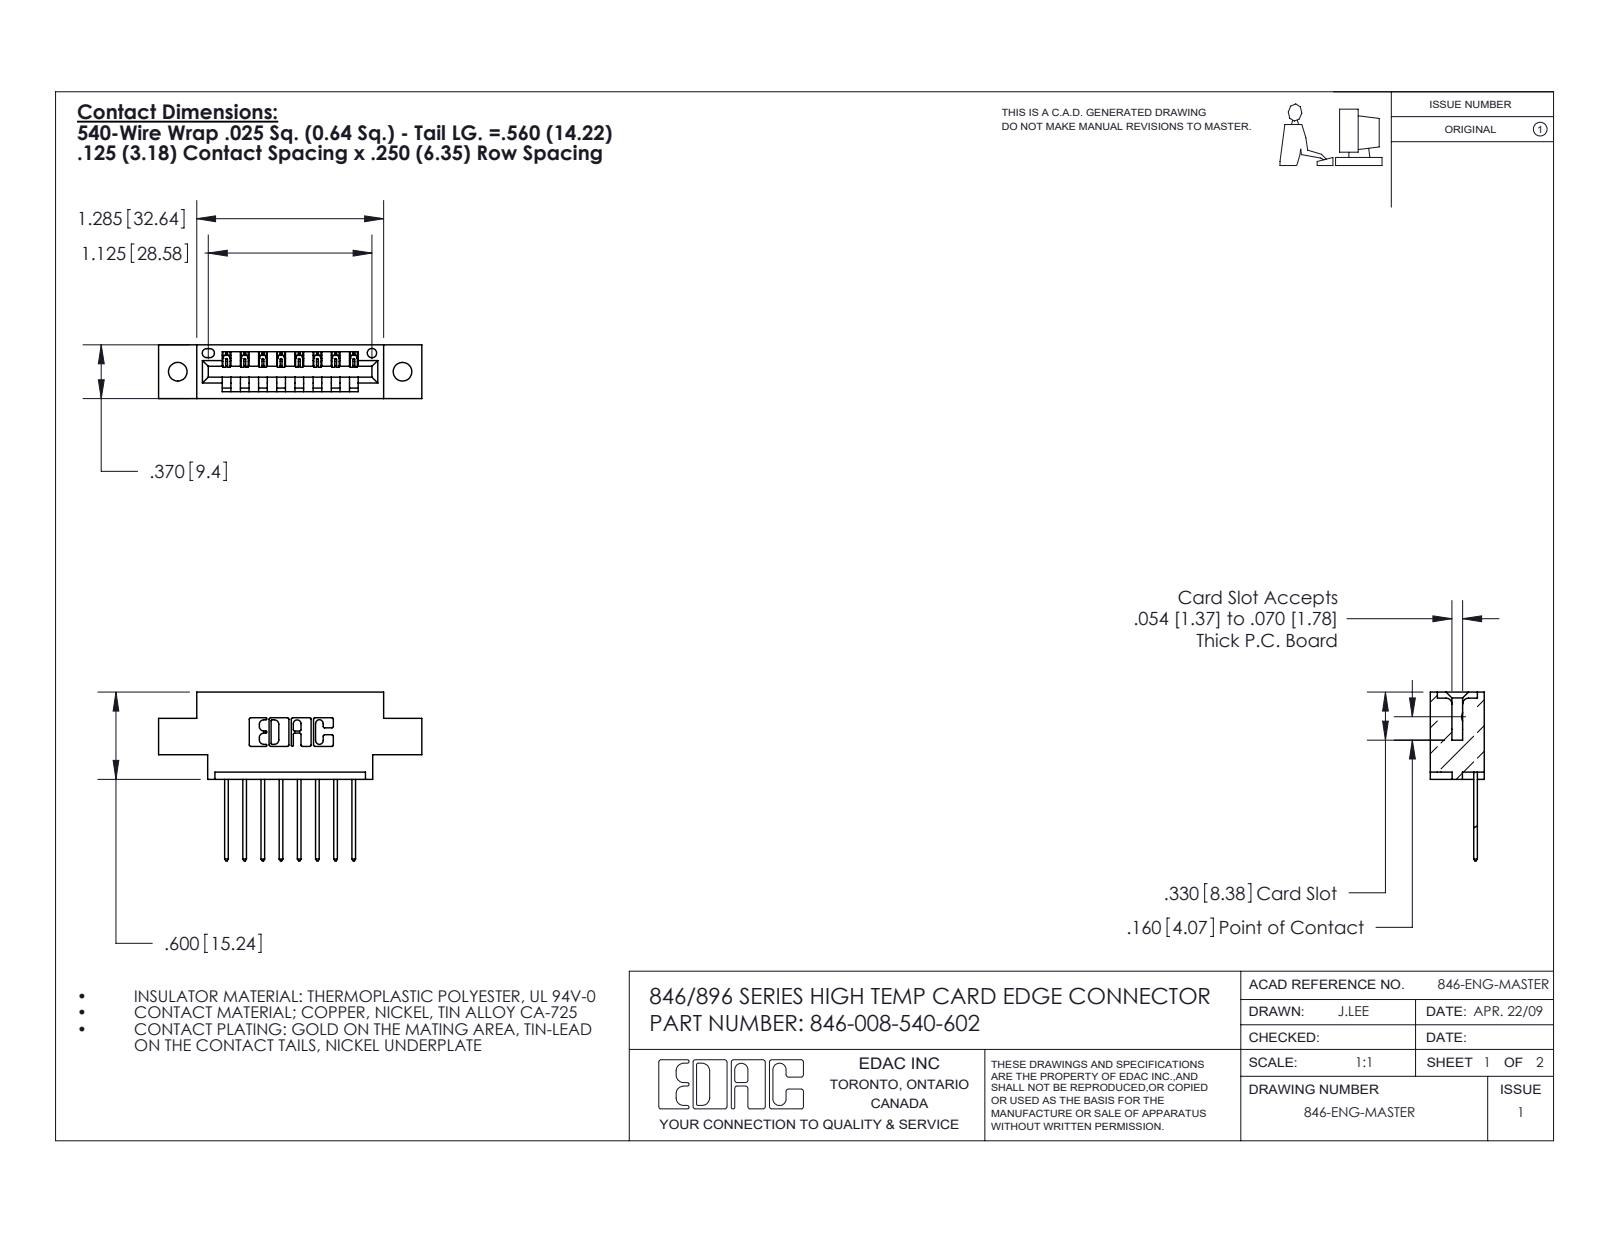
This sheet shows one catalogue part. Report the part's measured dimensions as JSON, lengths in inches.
{"part_name": "346-008-540-602; 346 Part_0.170 Offset - 0.128 Dia; 345-292-001_345-293-140", "step_written_by": "SolidWorks 2016 (CONFIG_CONTROL_DESIGN)", "units": "inches", "bodies": {"solids": 9, "faces": 590, "planar": 400, "cylindrical": 190, "other": 0}, "overall_size": [1.81, 1.16, 0.37], "volume_in3": 0.243, "surface_area_in2": 7.104, "round_holes": [[0.128, 2], [0.064, 1]], "partial_cylinders_radius": [[0.01, 22], [0.006, 16], [0.01, 16], [0.007, 6], [0.031, 6], [0.026, 3], [0.031, 2], [0.04, 2]], "face_to_face_distances": [0.25, 0.37, 0.048, 0.322, 0.072, 0.298, 0.025, 0.148, 0.222, 0.1], "hole_center_spacings": [0.246, 1.341, 1.545]}
